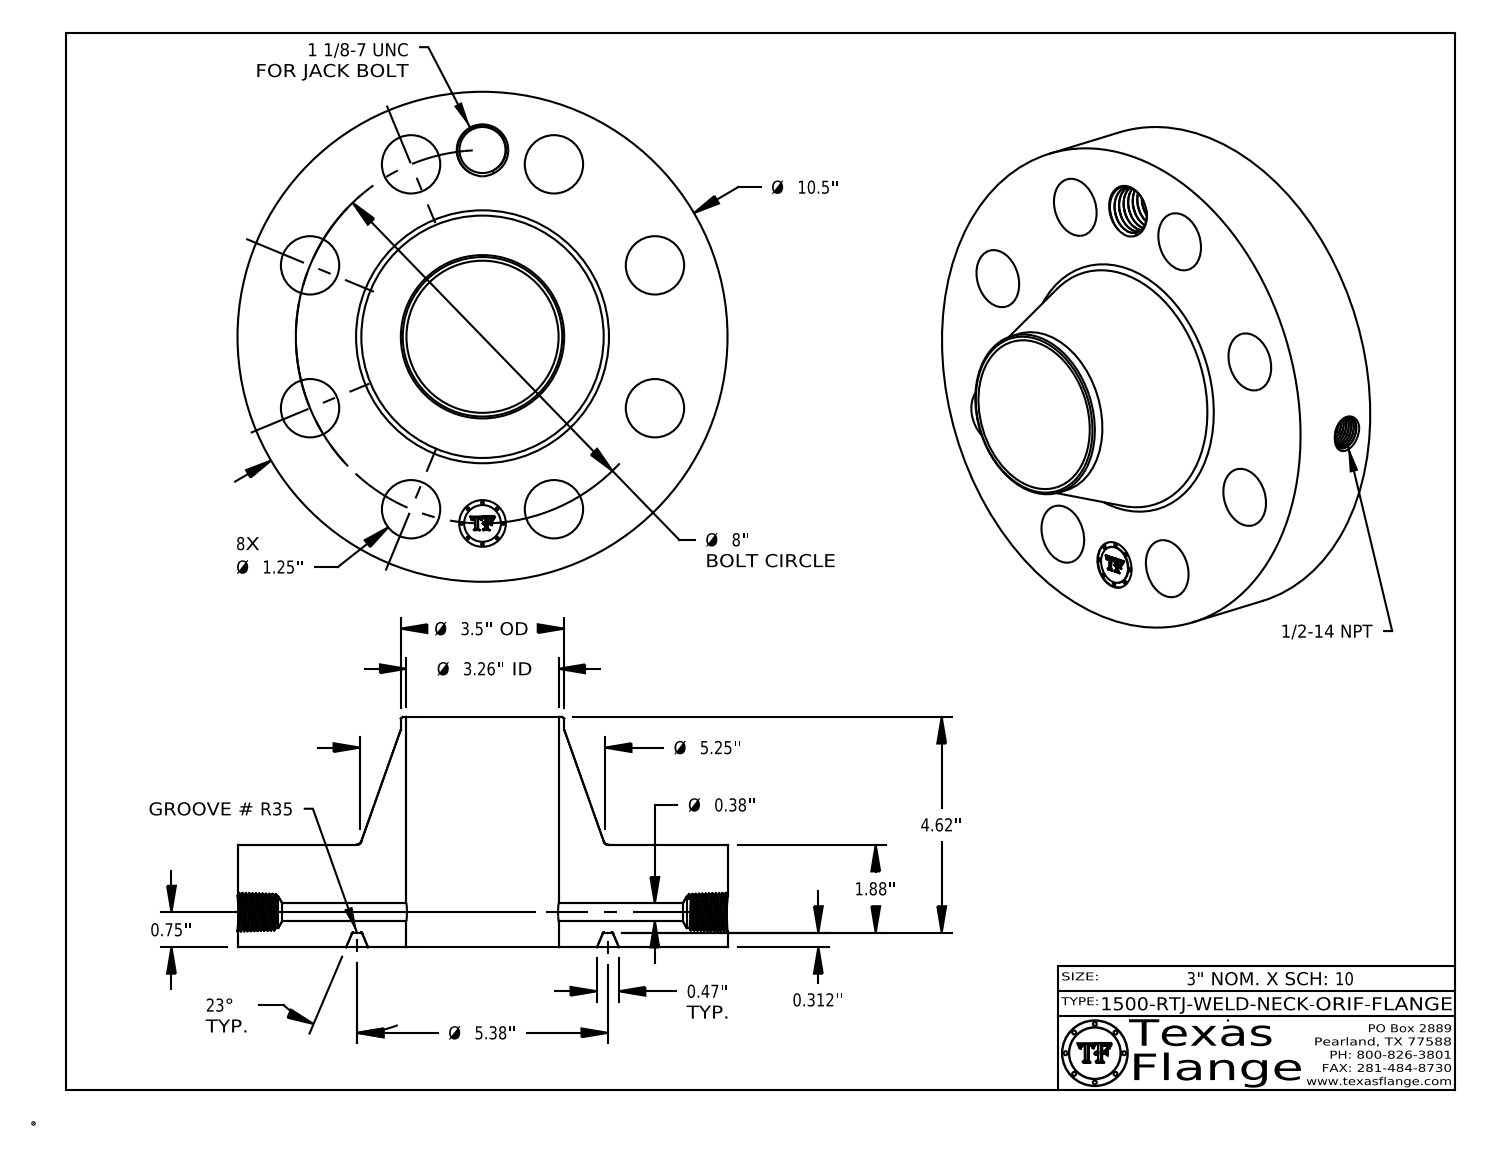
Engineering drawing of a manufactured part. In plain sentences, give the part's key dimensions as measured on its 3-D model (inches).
The part is named "1500-RTJ-WELD-NECK". Its 3-D file was written by "CATIA V5 STEP AP214 (AUTOMOTIVE_DESIGN)". It is 1 solid with 779 faces: 370 planar, 92 cylindrical and 317 other. Overall it measures 10.5 by 10.5 by 4.932 inches. Its volume is 162.3 cubic inches and its surface area 383.2 square inches. Round holes: 8 of diameter 1.25, 1 of diameter 0.375, 1 of diameter 0.672, 1 of diameter 0.984, 1 of diameter 1, 1 of diameter 3.26. Round bosses or shafts: 8 of diameter 0.061, 1 of diameter 10.5, 1 of diameter 3.5, 1 of diameter 0.788. The main face-to-face distances are 2.192, 0.312, 1.88, 4.932, 4.62, 2.74, 2.177, 1.865, 0.015, 2.755. The hole center spacings are 4, 5.657, 7.391, 1.561, 3.061, 3.062, 4.445, 6.652.
